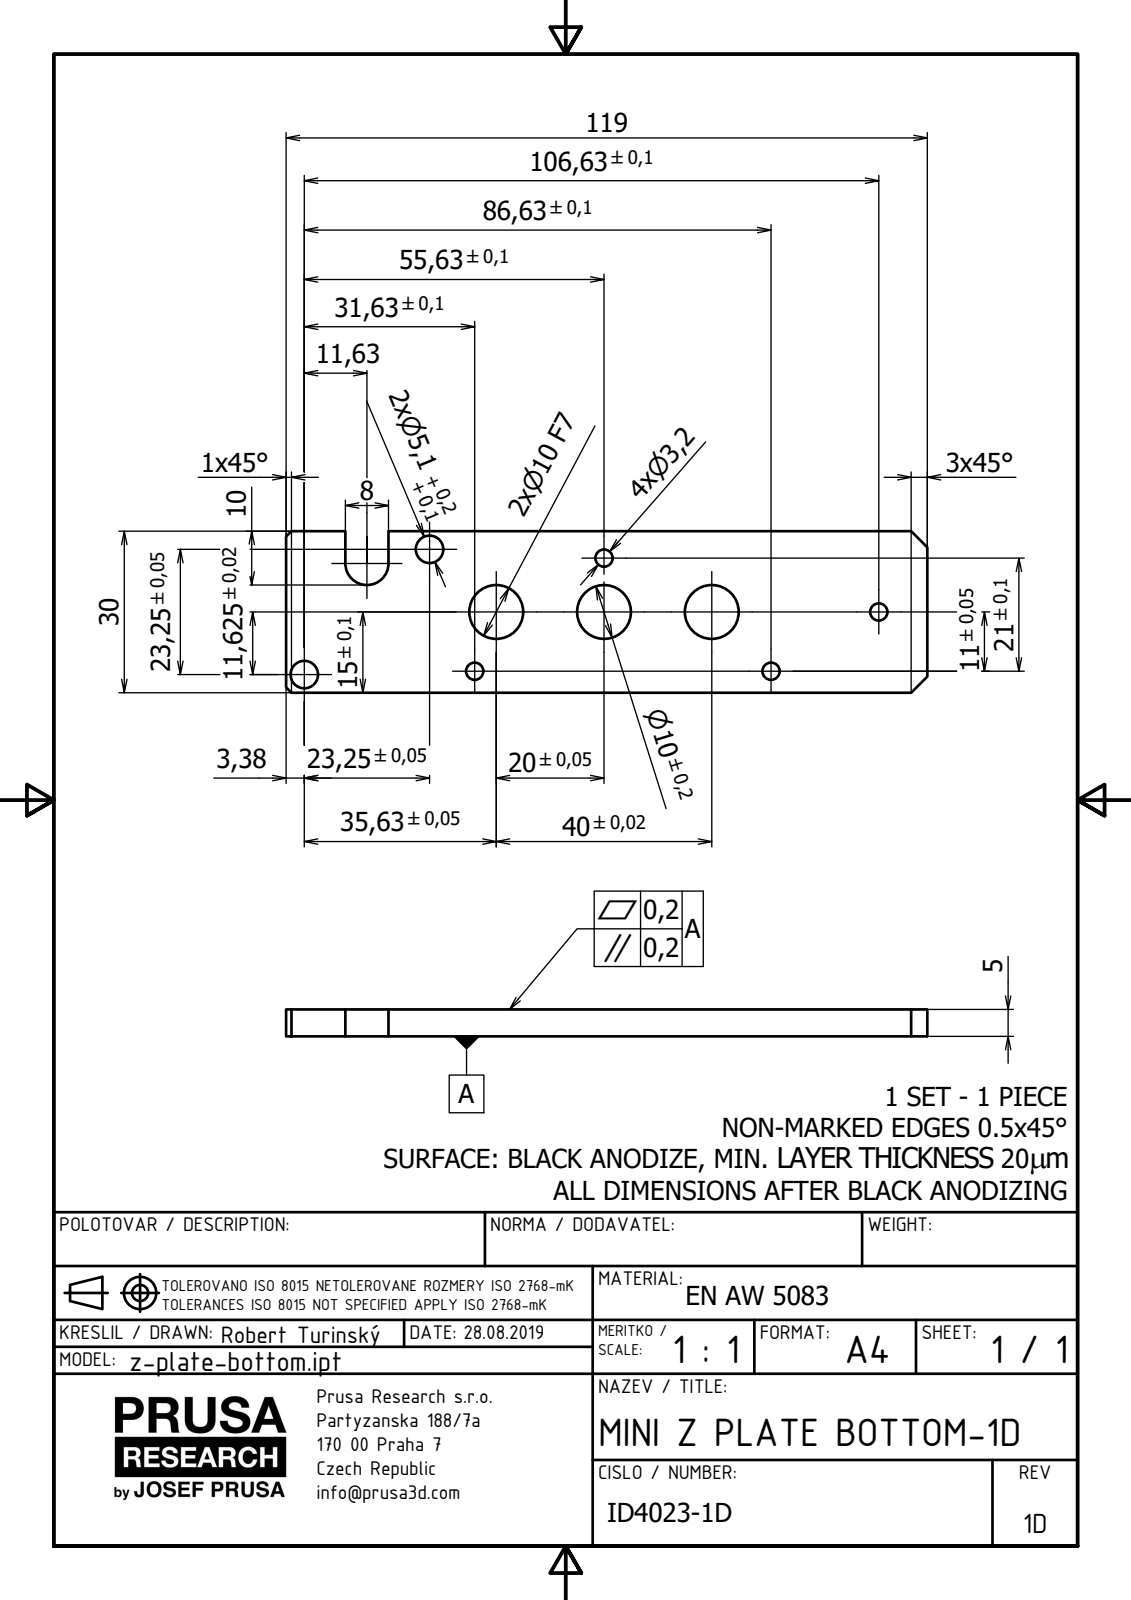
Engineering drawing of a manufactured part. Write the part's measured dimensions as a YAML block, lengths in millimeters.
part_name: "mini-z-plate-bottom"
step_written_by: "Autodesk Inventor 2019 (AUTOMOTIVE_DESIGN)"
units: millimeters
bodies: {solids: 1, faces: 23, planar: 13, cylindrical: 10, other: 0}
overall_size: [119, 30, 5]
volume: 15899
surface_area: 8738
round_holes:
  - {diameter: 3.2, count: 4}
  - {diameter: 10, count: 3}
  - {diameter: 5, count: 2}
partial_cylinders:
  - {radius: 4, count: 1}
face_to_face_distances: [5, 30, 119, 11, 19, 8, 108, 100, 102.51]
hole_center_spacings: [20, 22.36, 10, 11.7, 15.56, 16.98, 22.83, 24.12]
